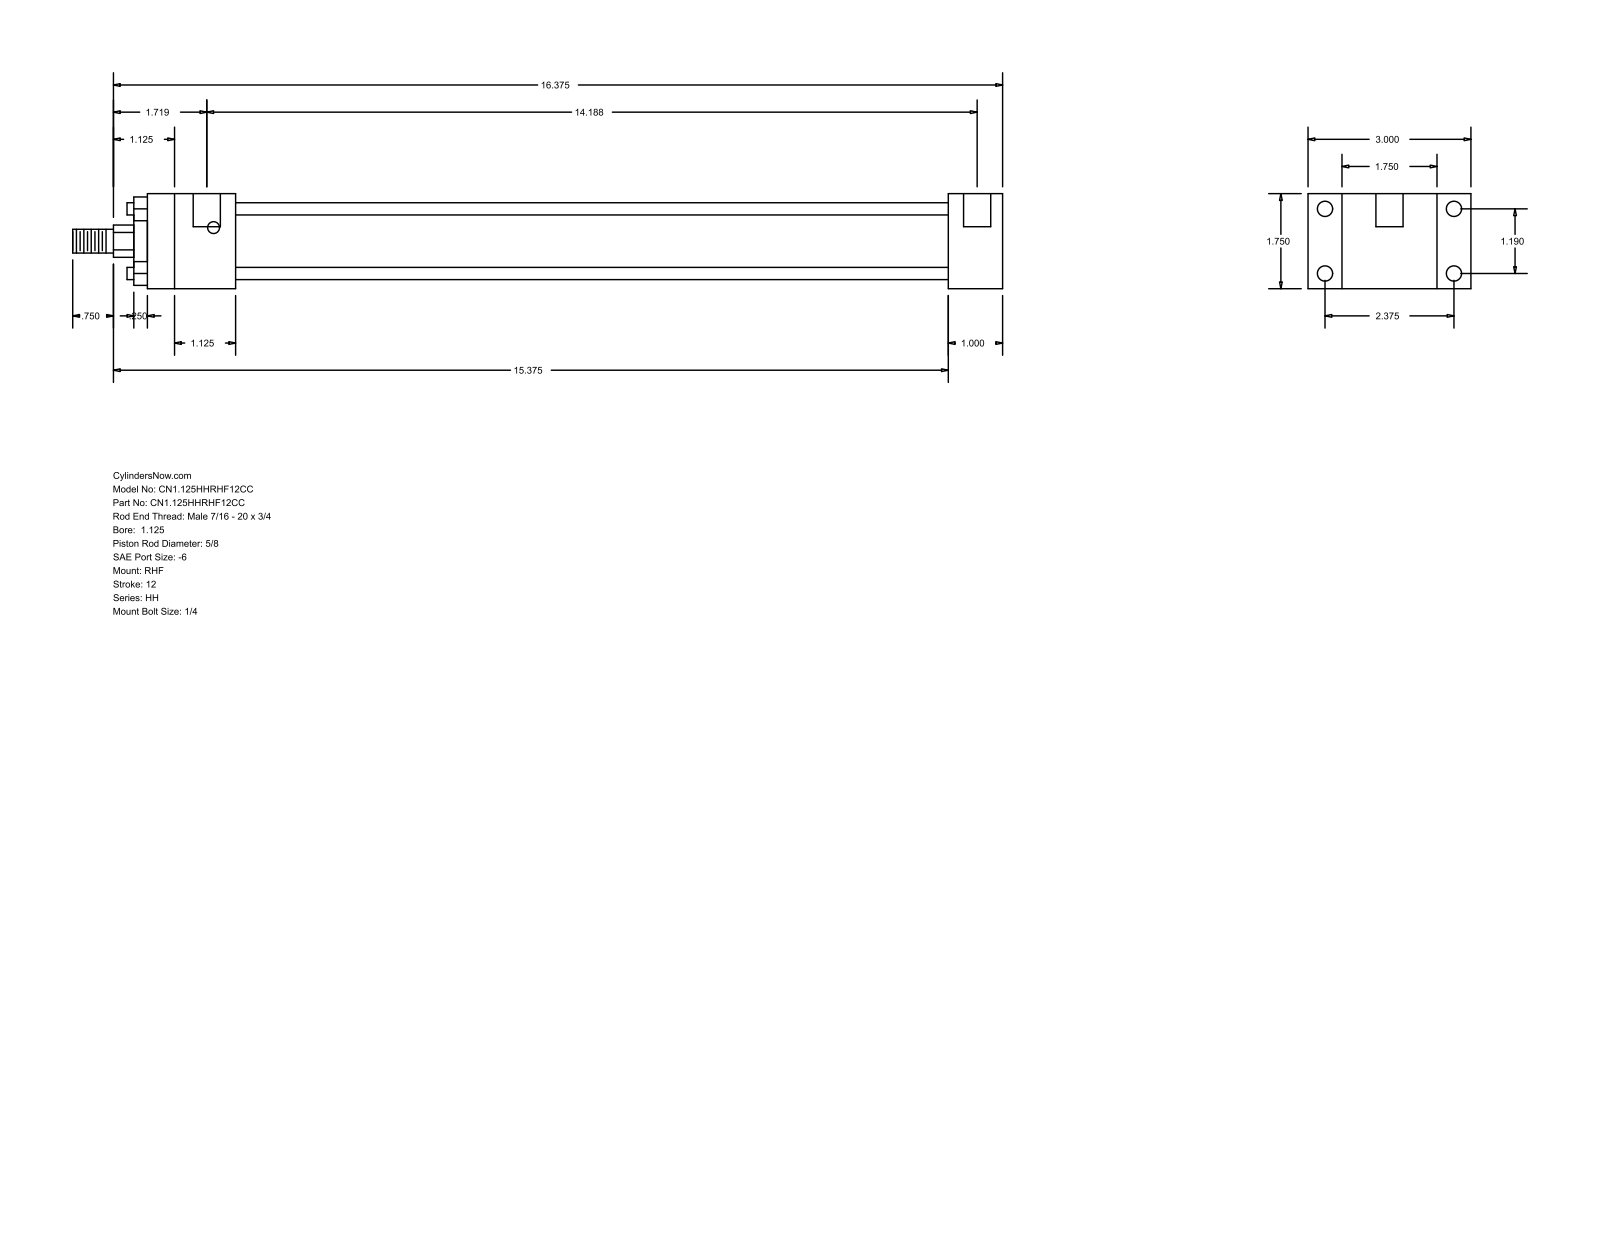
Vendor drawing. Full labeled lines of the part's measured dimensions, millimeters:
Part name (STEP PRODUCT): HH_RHF__0112_0.625
STEP written by: GSSL Pune (CONFIG_CONTROL_DESIGN)
Units: millimetres
Bodies: 0 solids, 88 faces (60 planar, 28 cylindrical, 0 other)
Overall size (bounding box): 434.98 × 76.2 × 44.45
Round holes (diameter × count): ⌀5.56 ×4, ⌀7.14 ×4, ⌀12.7 ×2
Round bosses / shafts (diameter × count): ⌀5.71 ×4, ⌀34.92 ×1, ⌀28.57 ×1, ⌀15.88 ×1, ⌀11.11 ×1
Partial cylindrical surfaces — rounded edges, fillets, slot ends (radius × count): R7.54 ×1
Main face-to-face distances: 44.46, 15.87, 60.33, 25.41, 76.2, 333.37, 358.78, 41.27, 374.64, 400.05
Hole centre spacings: 30.22, 60.32, 67.47, 357.19, 3.17, 360.36
